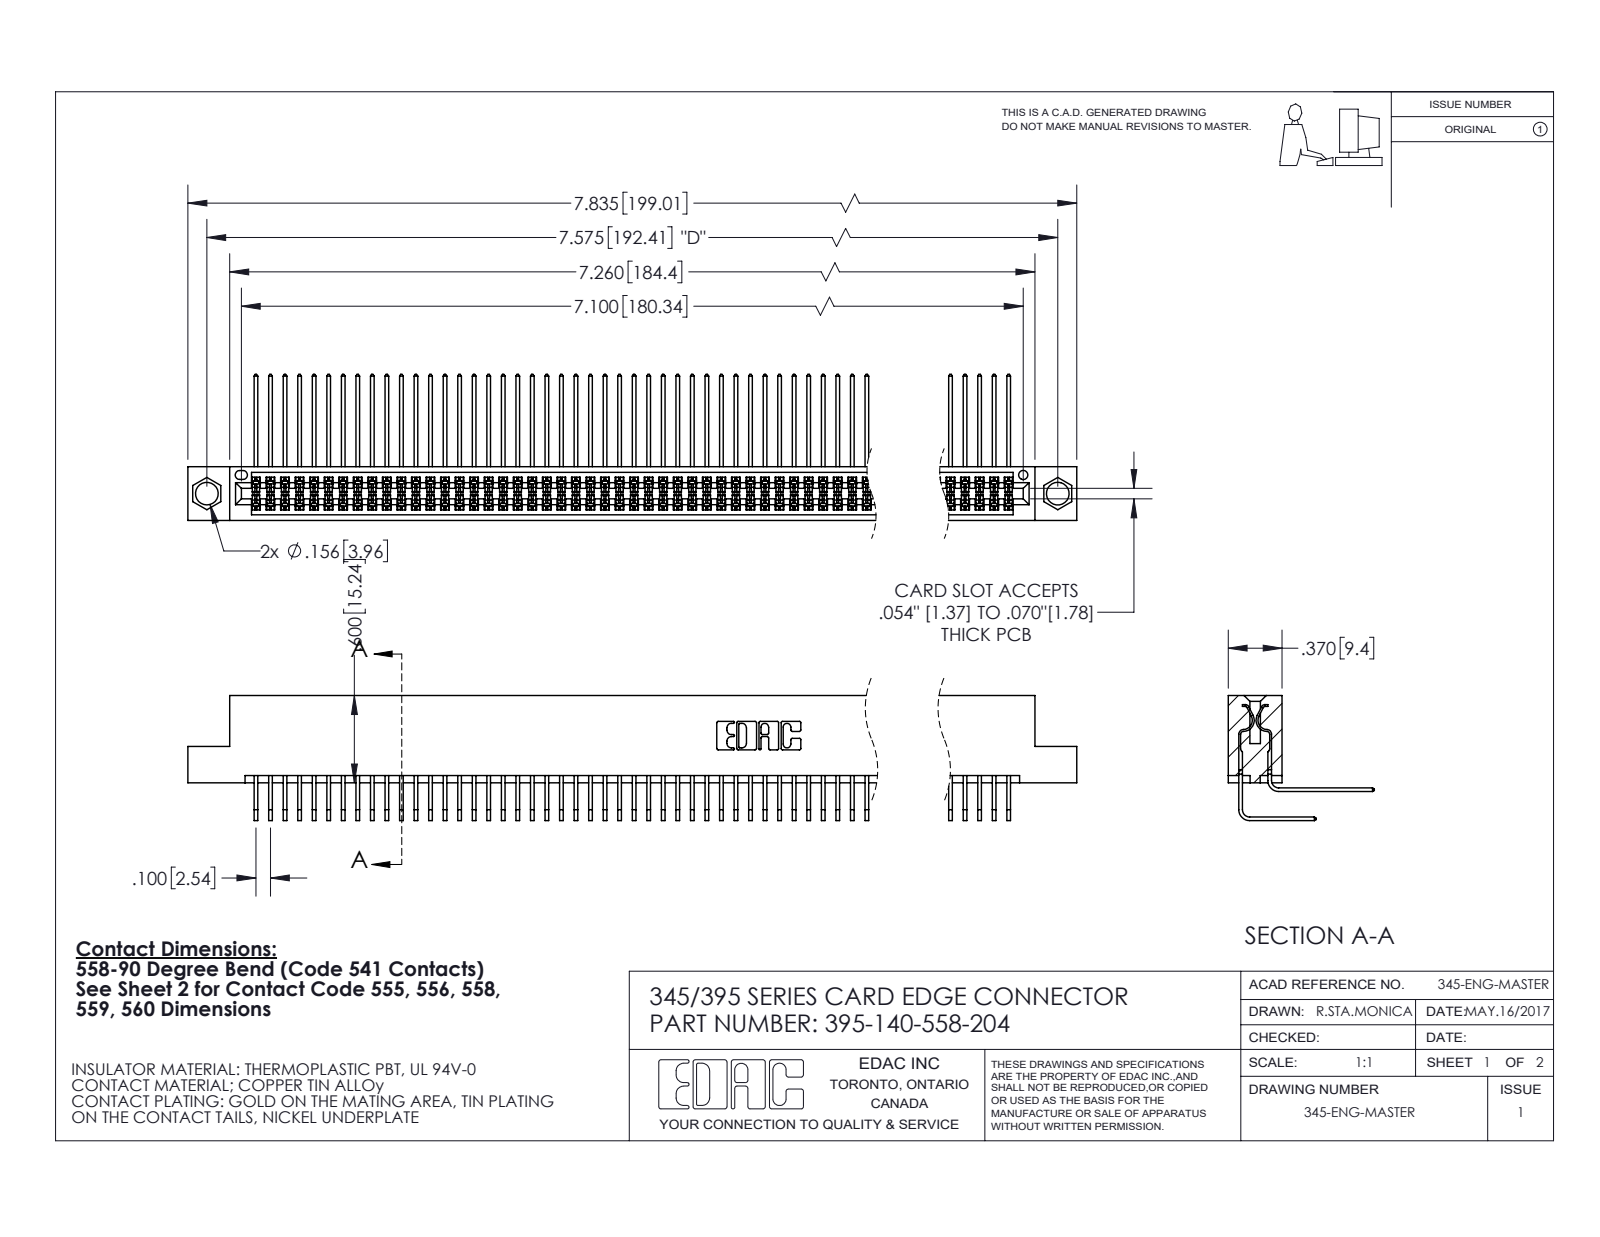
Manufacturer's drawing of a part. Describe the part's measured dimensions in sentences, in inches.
The part is named "395-140-558-204; 345-292-001_558 559 Tail - 1; 345 Part_Flush Mounting Lugs - 0.156 Dia-TI; 345-292-001_558 Tail - 2". Its 3-D file was written by "SolidWorks 2020 (CONFIG_CONTROL_DESIGN)". It is 141 solids with 7420 faces: 4994 planar, 2426 cylindrical and 0 other. Overall it measures 7.835 by 1.005 by 0.859 inches. Its volume is 1.238 cubic inches and its surface area 52.99 square inches. Round holes: 2 of diameter 0.156, 1 of diameter 0.064. Partial cylindrical surfaces (rounded edges, fillets, slot ends): 210 of radius 0.006, 22 of radius 0.01, 6 of radius 0.007, 6 of radius 0.031, 3 of radius 0.026, 2 of radius 0.014, 2 of radius 0.019, 2 of radius 0.022. The main face-to-face distances are 0.072, 0.298, 0.2, 0.37, 0.098, 0.272, 0.025, 0.225, 0.025, 0.175. The hole center spacings are 0.27, 7.339, 7.575.
